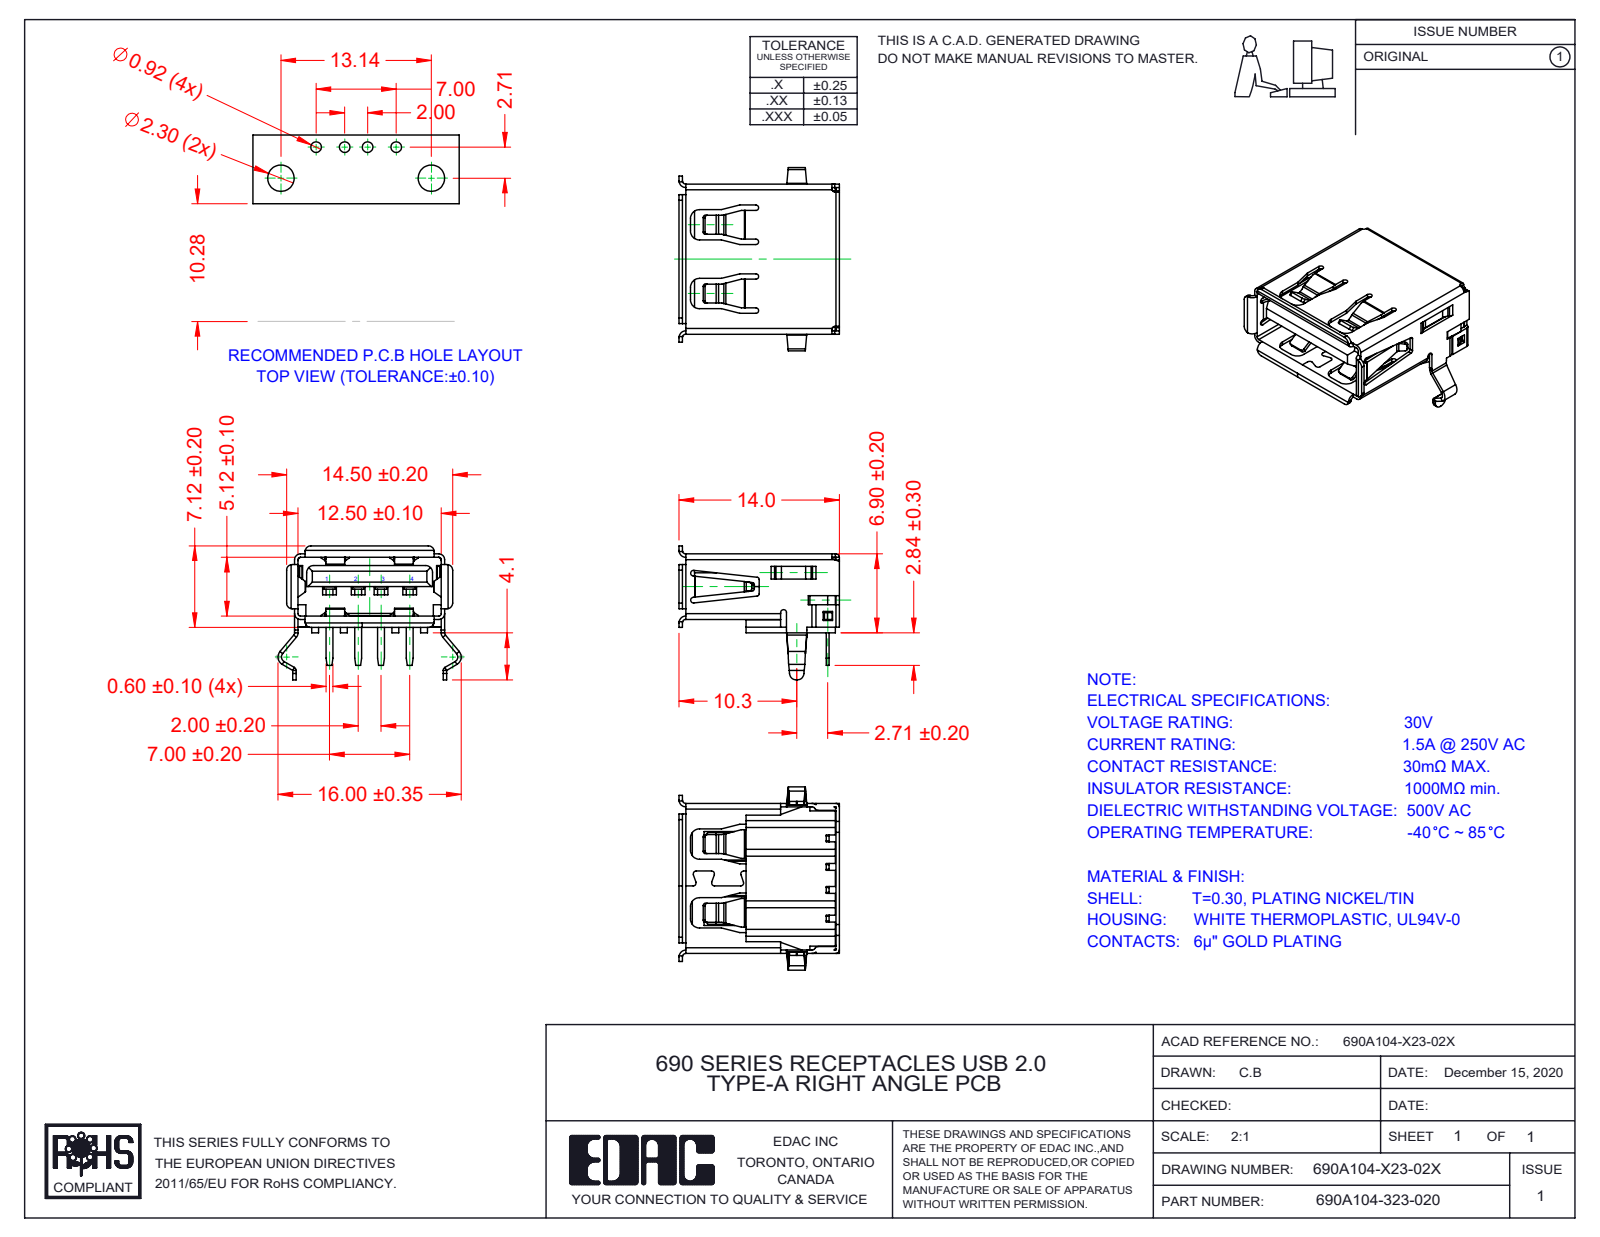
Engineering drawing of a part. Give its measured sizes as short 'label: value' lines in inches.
name: 690A104-123-020; Insulator 690A104-X23-02X_White; Shell 690A104-X23-02X; Contact 690A104-X23-02X
written by: SolidWorks 2020 (AUTOMOTIVE_DESIGN)
unit: in
bodies: 6 solids, 869 faces (656 planar, 187 cylindrical, 26 other)
size: 0.63 × 0.551 × 0.461
volume: 0.035 in³; area: 3.303 in²
rounds: 30× R0.008, 24× R0.02, 18× R0.012, 12× R0.024, 10× R0.01, 8× R0.004, 8× R0.031, 4× R0.009
face distances: 0.213, 0.202, 0.504, 0.04, 0.061, 0.05, 0.022, 0.028, 0.174, 0.164
